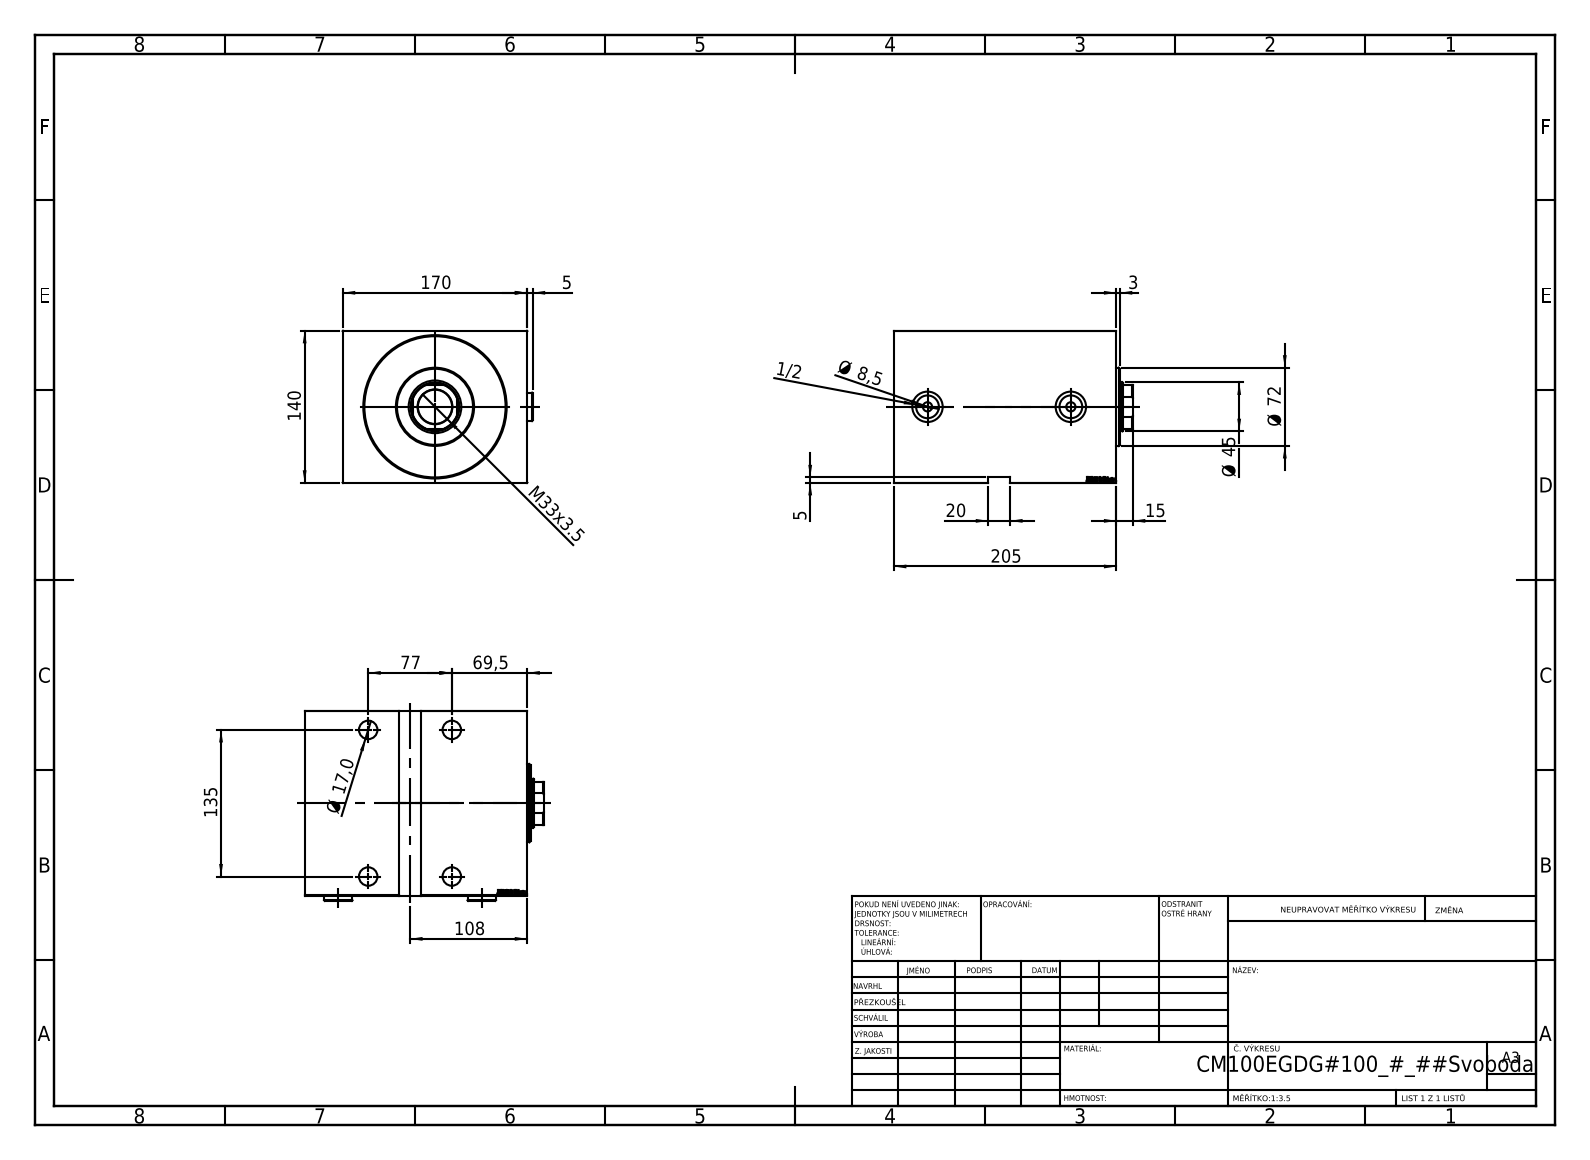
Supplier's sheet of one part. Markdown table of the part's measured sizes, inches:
| quantity | value |
| --- | --- |
| part name | V450CM_E_Body; V450CM_E_VCP; V450CM_VC_B; Zatka_OIL_PORT |
| STEP written by | SolidWorks 2019 (CONFIG_CONTROL_DESIGN) |
| units | inches |
| bodies | 5 solids, 912 faces (446 planar, 68 cylindrical, 398 other) |
| overall size | 8.661 × 6.886 × 5.512 |
| volume | 248.3 in³ |
| surface area | 561.5 in² |
| round holes (diameter × count) | 0.669 × 4, 0.984 × 4, 0.335 × 2, 0.825 × 2, 1.102 × 2, 1.24 × 1, 1.772 × 1, 1.909 × 1, 3.937 × 1, 5.118 × 1 |
| round bosses / shafts (diameter × count) | 1.024 × 2, 4.016 × 1, 2.835 × 1 |
| partial cylindrical surfaces (radius × count) | 0.866 × 1 |
| main face-to-face distances | 5.512, 6.693, 8.071, 1.024, 7.047, 0.197, 7.874, 6.85, 3.543, 7.417 |
| hole center spacings | 3.031, 5.315, 6.119, 5.197 |
